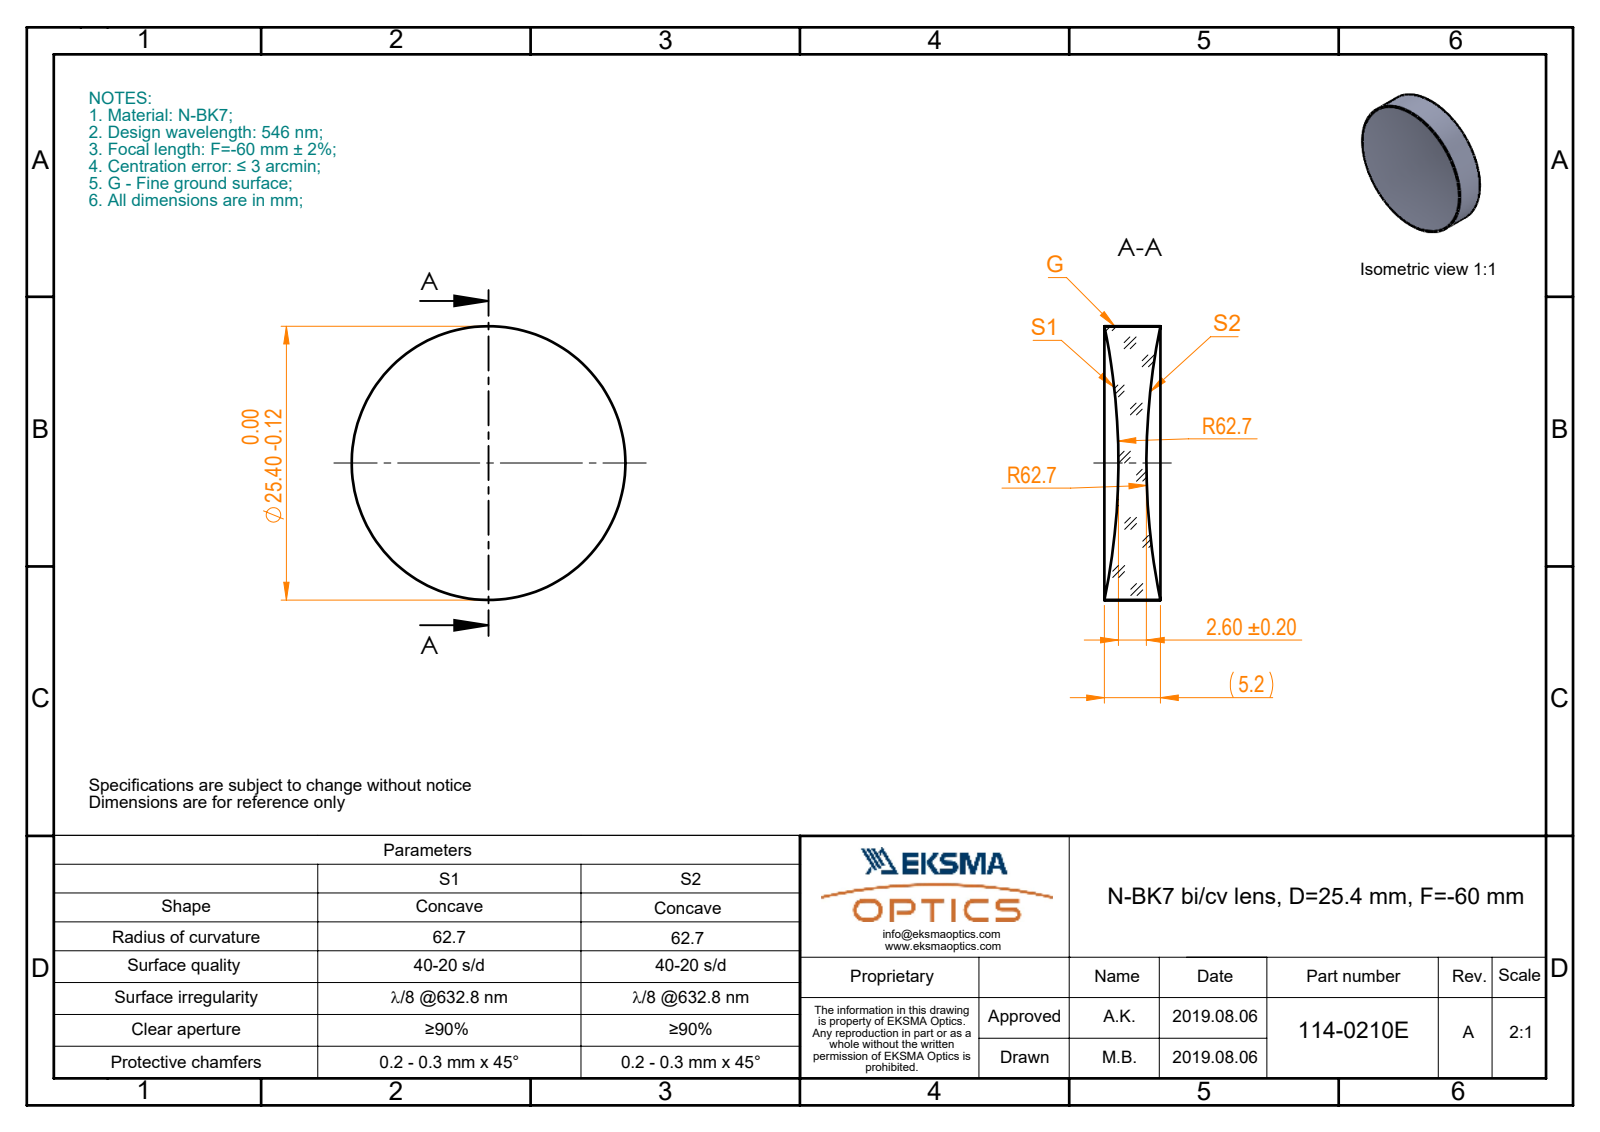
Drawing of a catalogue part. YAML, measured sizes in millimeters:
part_name: "114-0210E BK7 bi-cv 25.4 F-60"
step_written_by: "SolidWorks 2017 (CONFIG_CONTROL_DESIGN)"
units: millimeters
bodies: {solids: 1, faces: 6, planar: 0, cylindrical: 2, other: 4}
overall_size: [25.4, 25.4, 5.2]
volume: 1974
surface_area: 1439
round_bosses_or_shafts:
  - {diameter: 25.4, count: 1}
